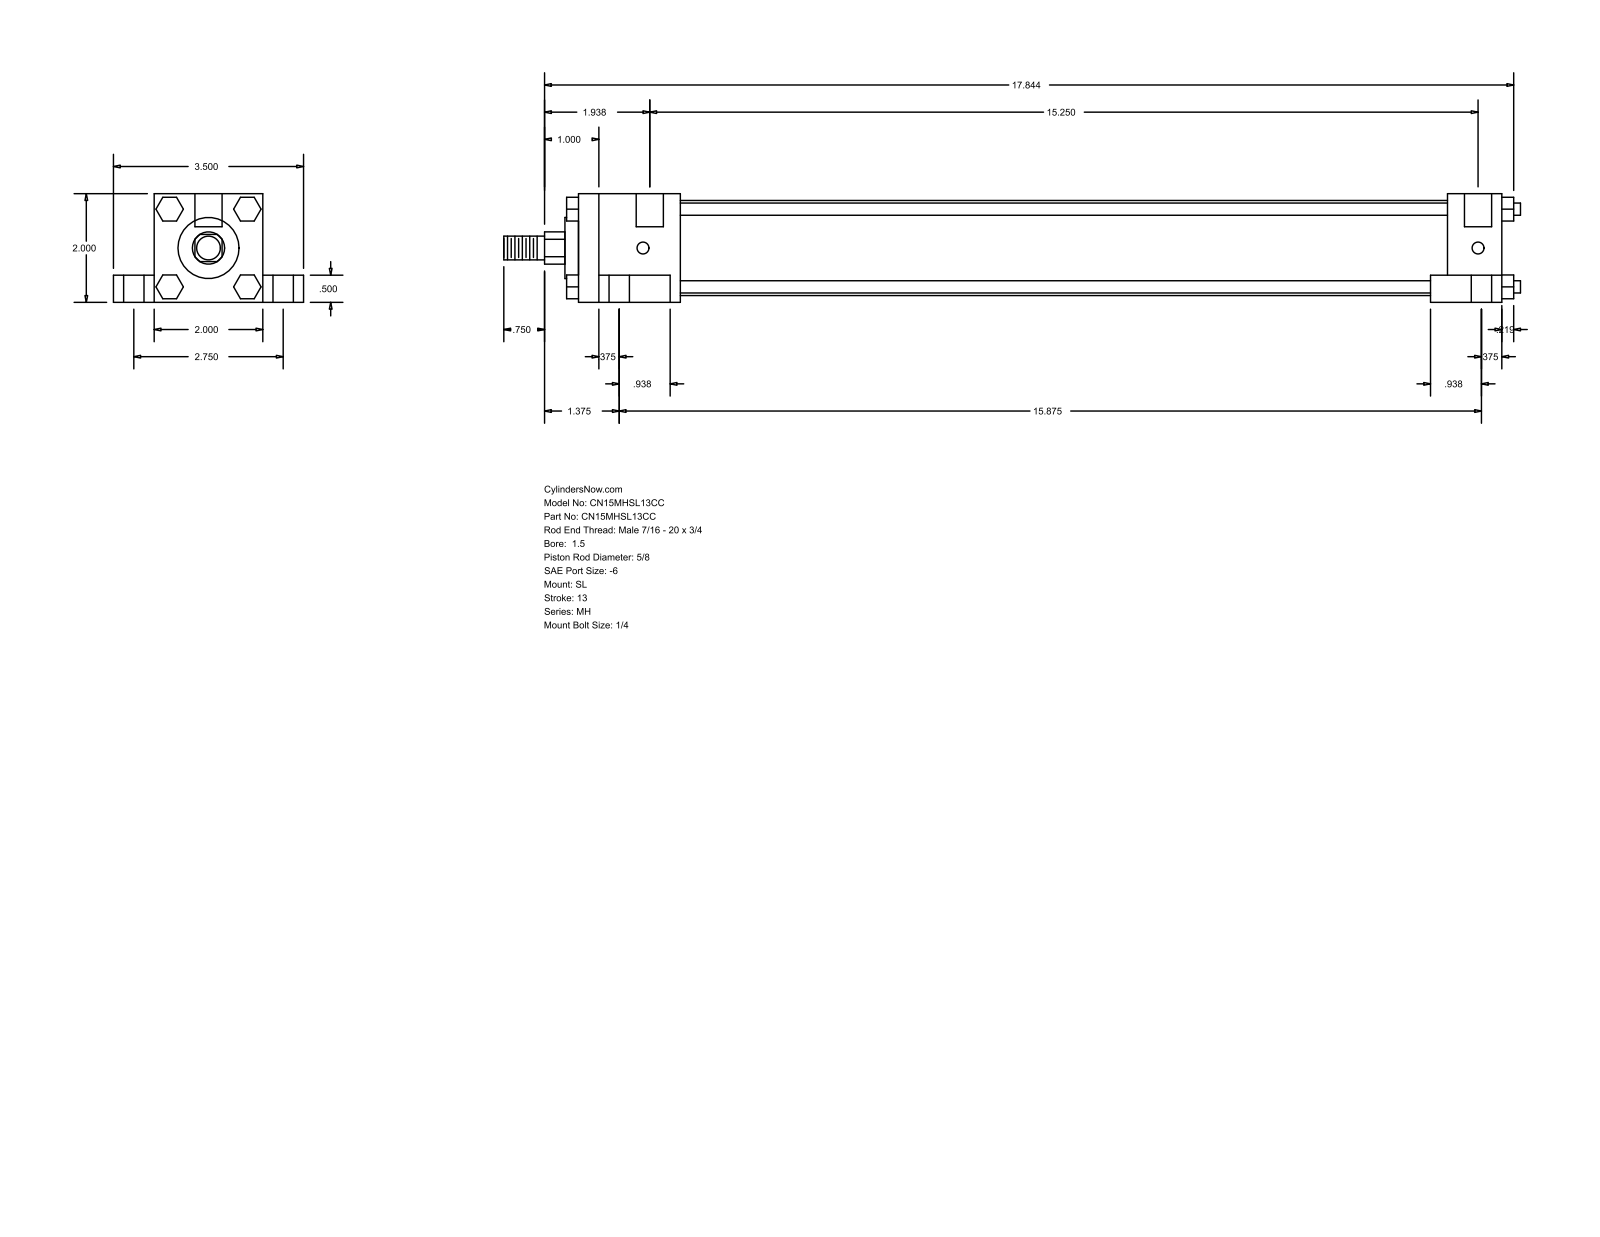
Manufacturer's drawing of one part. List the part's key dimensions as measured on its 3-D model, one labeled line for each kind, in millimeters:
Part name (STEP PRODUCT): MH_SL__0150_0.625
STEP written by: GSSL Pune (CONFIG_CONTROL_DESIGN)
Units: millimetres
Bodies: 0 solids, 148 faces (112 planar, 36 cylindrical, 0 other)
Overall size (bounding box): 475.46 × 88.9 × 50.8
Round holes (diameter × count): ⌀5.56 ×4, ⌀9.53 ×4, ⌀15.88 ×4, ⌀12.7 ×2
Round bosses / shafts (diameter × count): ⌀5.71 ×4, ⌀44.45 ×1, ⌀28.57 ×1, ⌀15.88 ×1, ⌀11.11 ×1
Partial cylindrical surfaces — rounded edges, fillets, slot ends (radius × count): R7.54 ×1
Main face-to-face distances: 50.8, 38.1, 19.05, 12.7, 69.85, 431.8, 9.52, 33.34, 388.94, 406.39
Hole centre spacings: 34.96, 36.65, 37.73, 69.84, 390.5, 390.52, 393.66, 403.16
